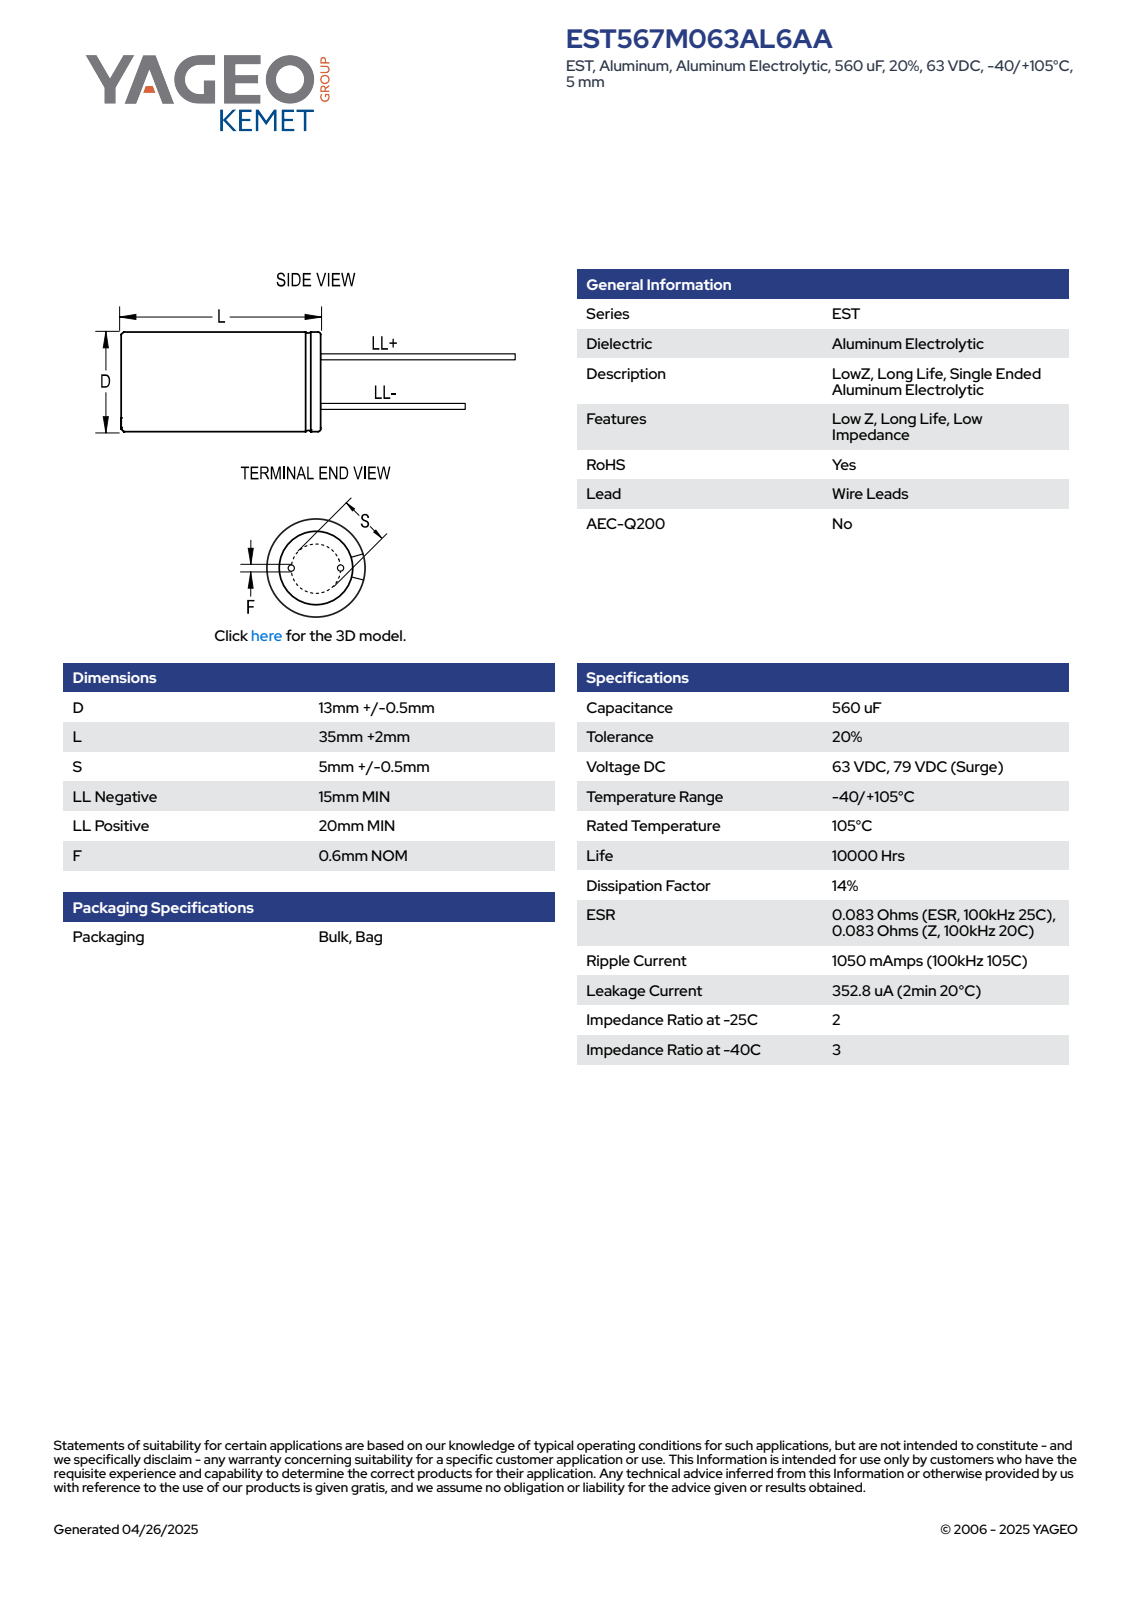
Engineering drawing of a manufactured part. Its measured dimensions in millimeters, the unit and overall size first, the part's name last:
Units: millimetres
Overall size (bounding box): 57.01 × 13.5 × 13.5
Round bosses / shafts (diameter × count): ⌀0.6 ×2, ⌀13.5 ×1
Main face-to-face distances: 37, 37.01, 52.01, 57.01, 52, 57, 15, 20, 5, 1.81
Volume: 5 280 mm³ · Surface area: 1 963 mm²
Bodies: 4 solids, 75 faces (61 planar, 8 cylindrical, 6 other)
Part name (STEP PRODUCT): CAR_KLP_13X35_D13.5L37S5F0.6
STEP written by: SolidWorks 2014 (AUTOMOTIVE_DESIGN)
